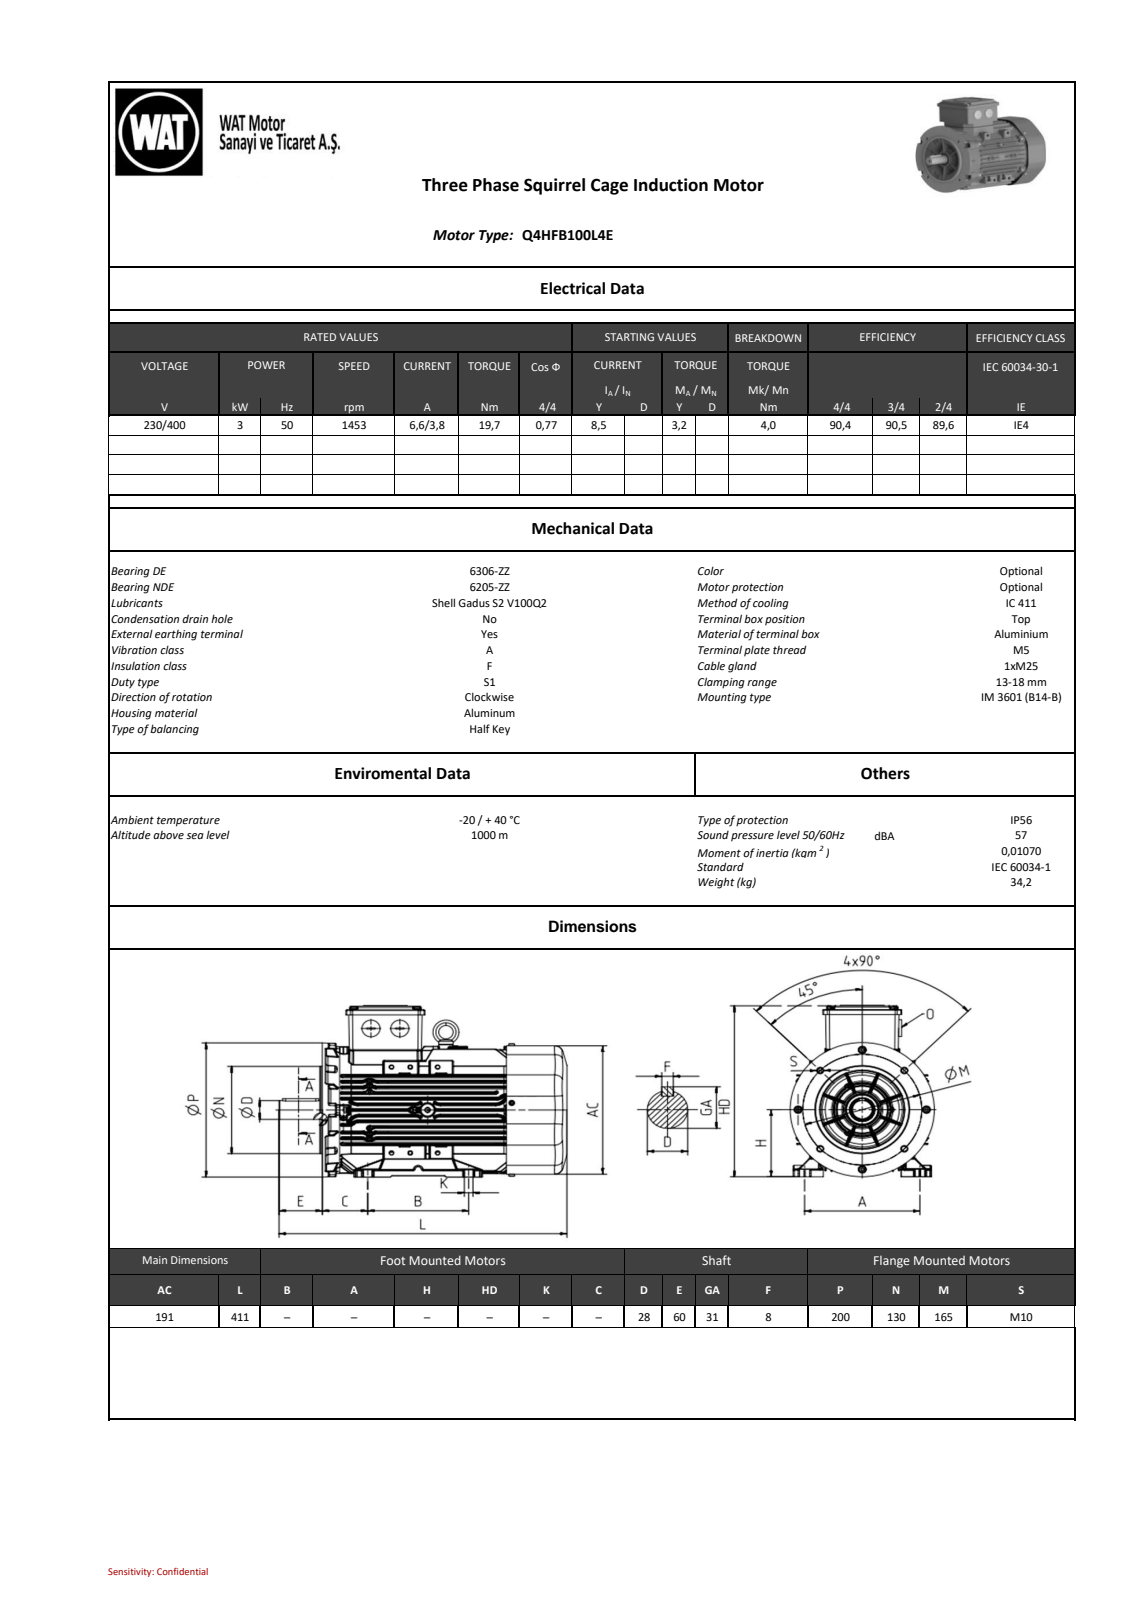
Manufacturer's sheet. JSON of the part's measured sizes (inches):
{"part_name": "QH100 B35 KTA-M2_stp_objects", "step_written_by": "SIEMENS PLM Software NX2206.8101 (AUTOMOTIVE_DESIGN)", "units": "inches", "bodies": {"solids": 0, "faces": 5435, "planar": 1185, "cylindrical": 2015, "other": 2235}, "overall_size": [16.191, 9.55, 7.874], "round_holes": [[0.335, 4], [0.453, 4], [0.394, 1], [0.413, 1], [0.472, 1], [1.728, 1], [1.736, 1], [2.047, 1], [2.26, 1], [2.835, 1], [3.071, 1], [3.504, 1]], "round_bosses_or_shafts": [[0.315, 8], [5.118, 1], [4.469, 1], [3.681, 1], [2.402, 1], [1.181, 1], [1.142, 1], [1.102, 1]], "partial_cylinders_radius": [[0.031, 561], [0.039, 512], [0.079, 82], [0.02, 53], [0.032, 52], [0.197, 36], [0.591, 26], [0.177, 16]], "face_to_face_distances": [0.336, 0.333, 0.333, 3.002, 0.666, 3.679, 1.007, 0.671, 3.019, 2.348], "hole_center_spacings": [2.595, 6.239, 3.248, 3.504, 4.594, 4.956, 6.496, 7.008]}
